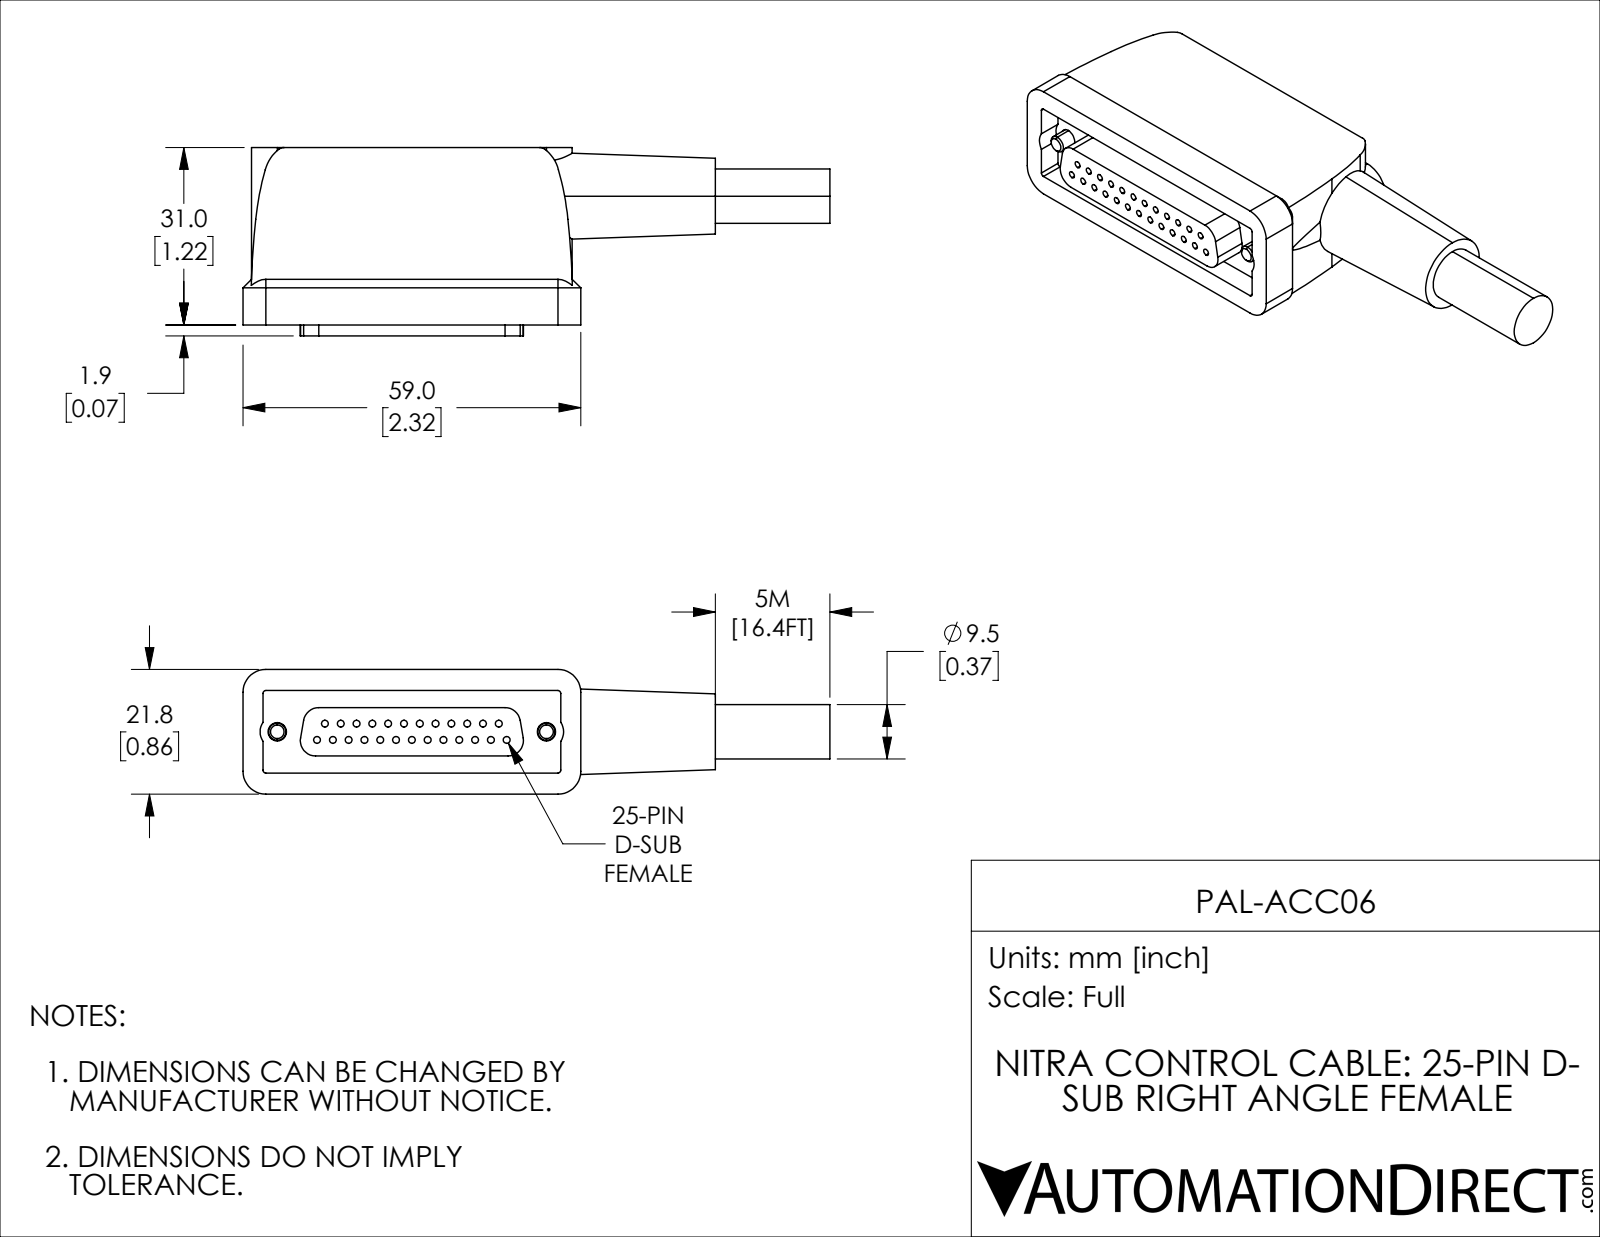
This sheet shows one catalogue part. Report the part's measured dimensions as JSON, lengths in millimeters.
{"part_name": "PAL-ACC06", "step_written_by": "SolidWorks 2019 (CONFIG_CONTROL_DESIGN)", "units": "millimeters", "bodies": {"solids": 1, "faces": 186, "planar": 71, "cylindrical": 101, "other": 14}, "overall_size": [102.5, 32.9, 21.8], "volume_mm3": 37542, "surface_area_mm2": 11486, "round_holes": [[1.2, 25], [3.2, 2], [5, 2]], "round_bosses_or_shafts": [[4.6, 2], [3, 2], [9.5, 1]], "partial_cylinders_radius": [[0.5, 4], [2.68, 4], [4, 4], [1.4, 2], [3, 2], [4.5, 2], [6.5, 2], [50, 2]], "face_to_face_distances": [18.8, 1.5, 20.3, 31, 4.1, 26.9, 3.7, 18.1, 2.2, 16.6], "hole_center_spacings": [3.16, 2.76, 5.02, 5.52, 7.46, 8.28, 10.07, 11.04]}
